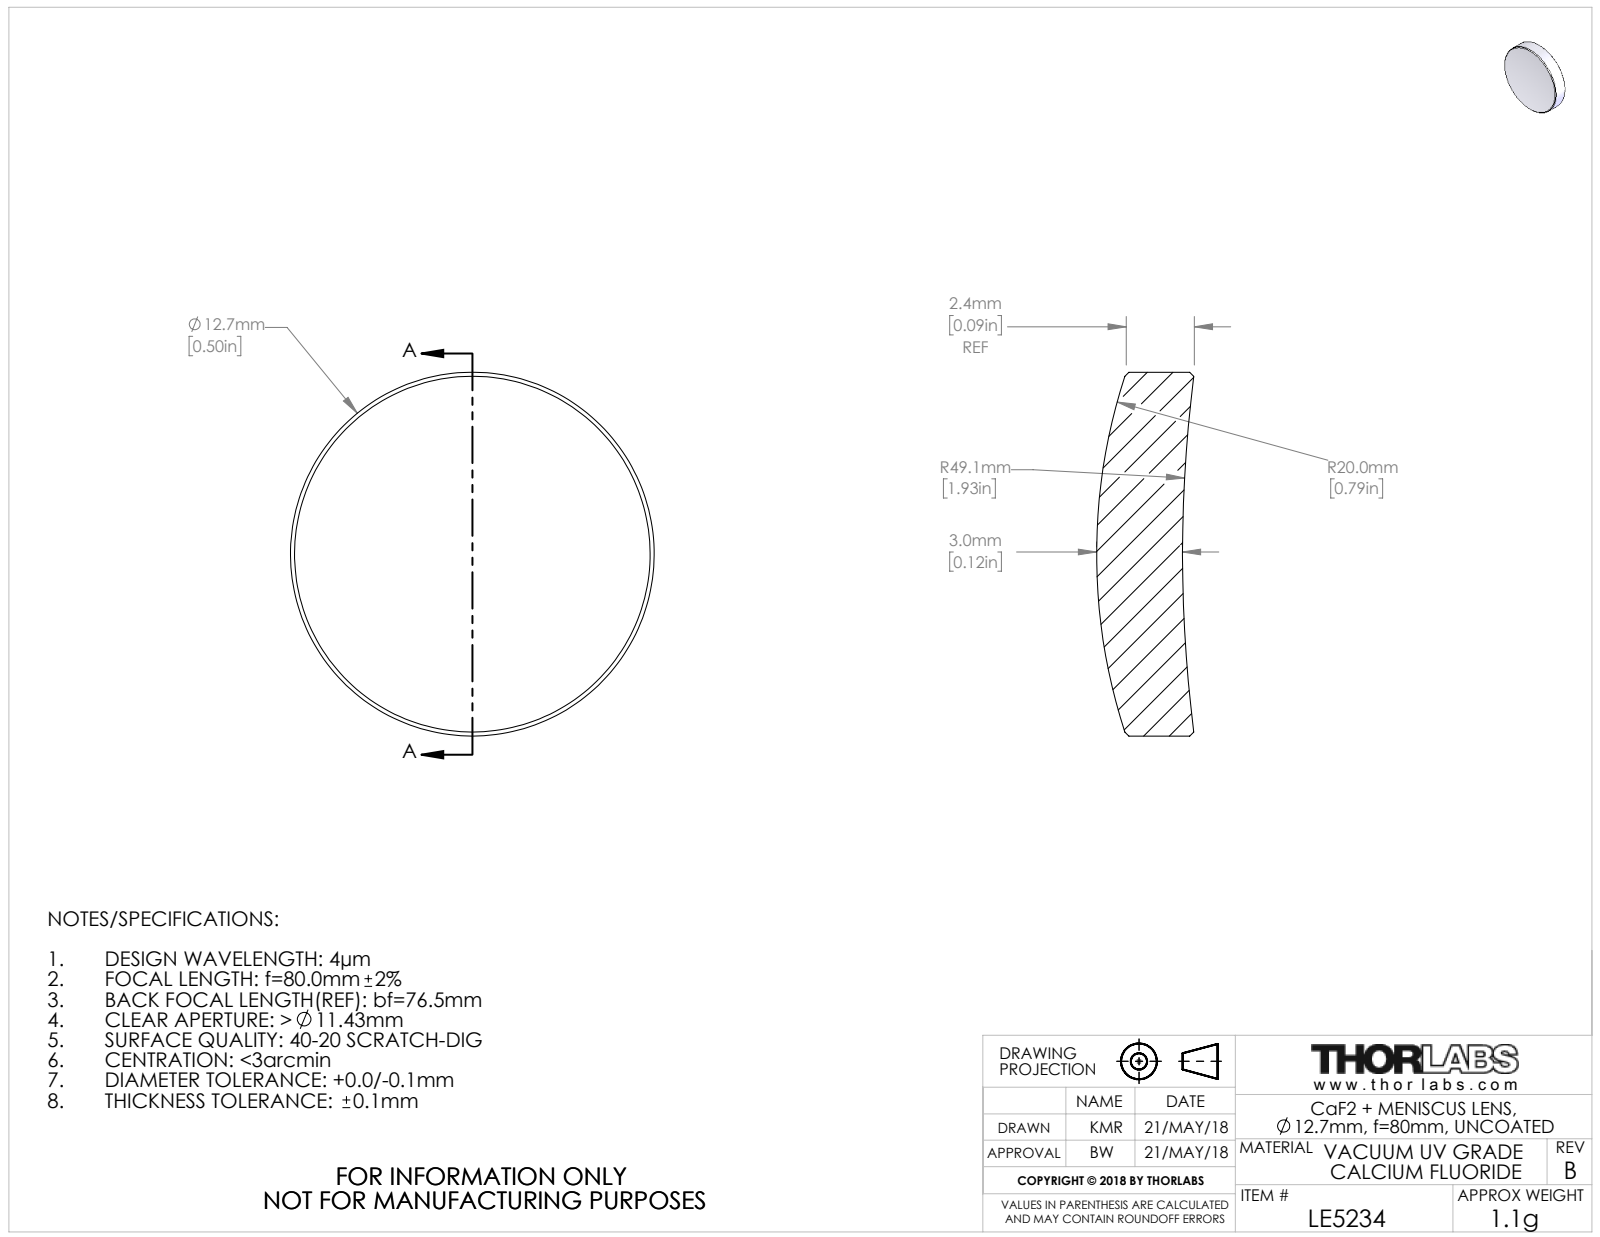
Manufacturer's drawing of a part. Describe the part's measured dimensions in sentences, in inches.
The part is named "21985-E0W". Its 3-D file was written by "SolidWorks 2016 (CONFIG_CONTROL_DESIGN)". It is 1 solid with 10 faces: 0 planar, 2 cylindrical and 8 other. Overall it measures 0.5 by 0.5 by 0.134 inches. Its volume is 0.021 cubic inches and its surface area 0.537 square inches. Round bosses or shafts: 1 of diameter 0.5.
